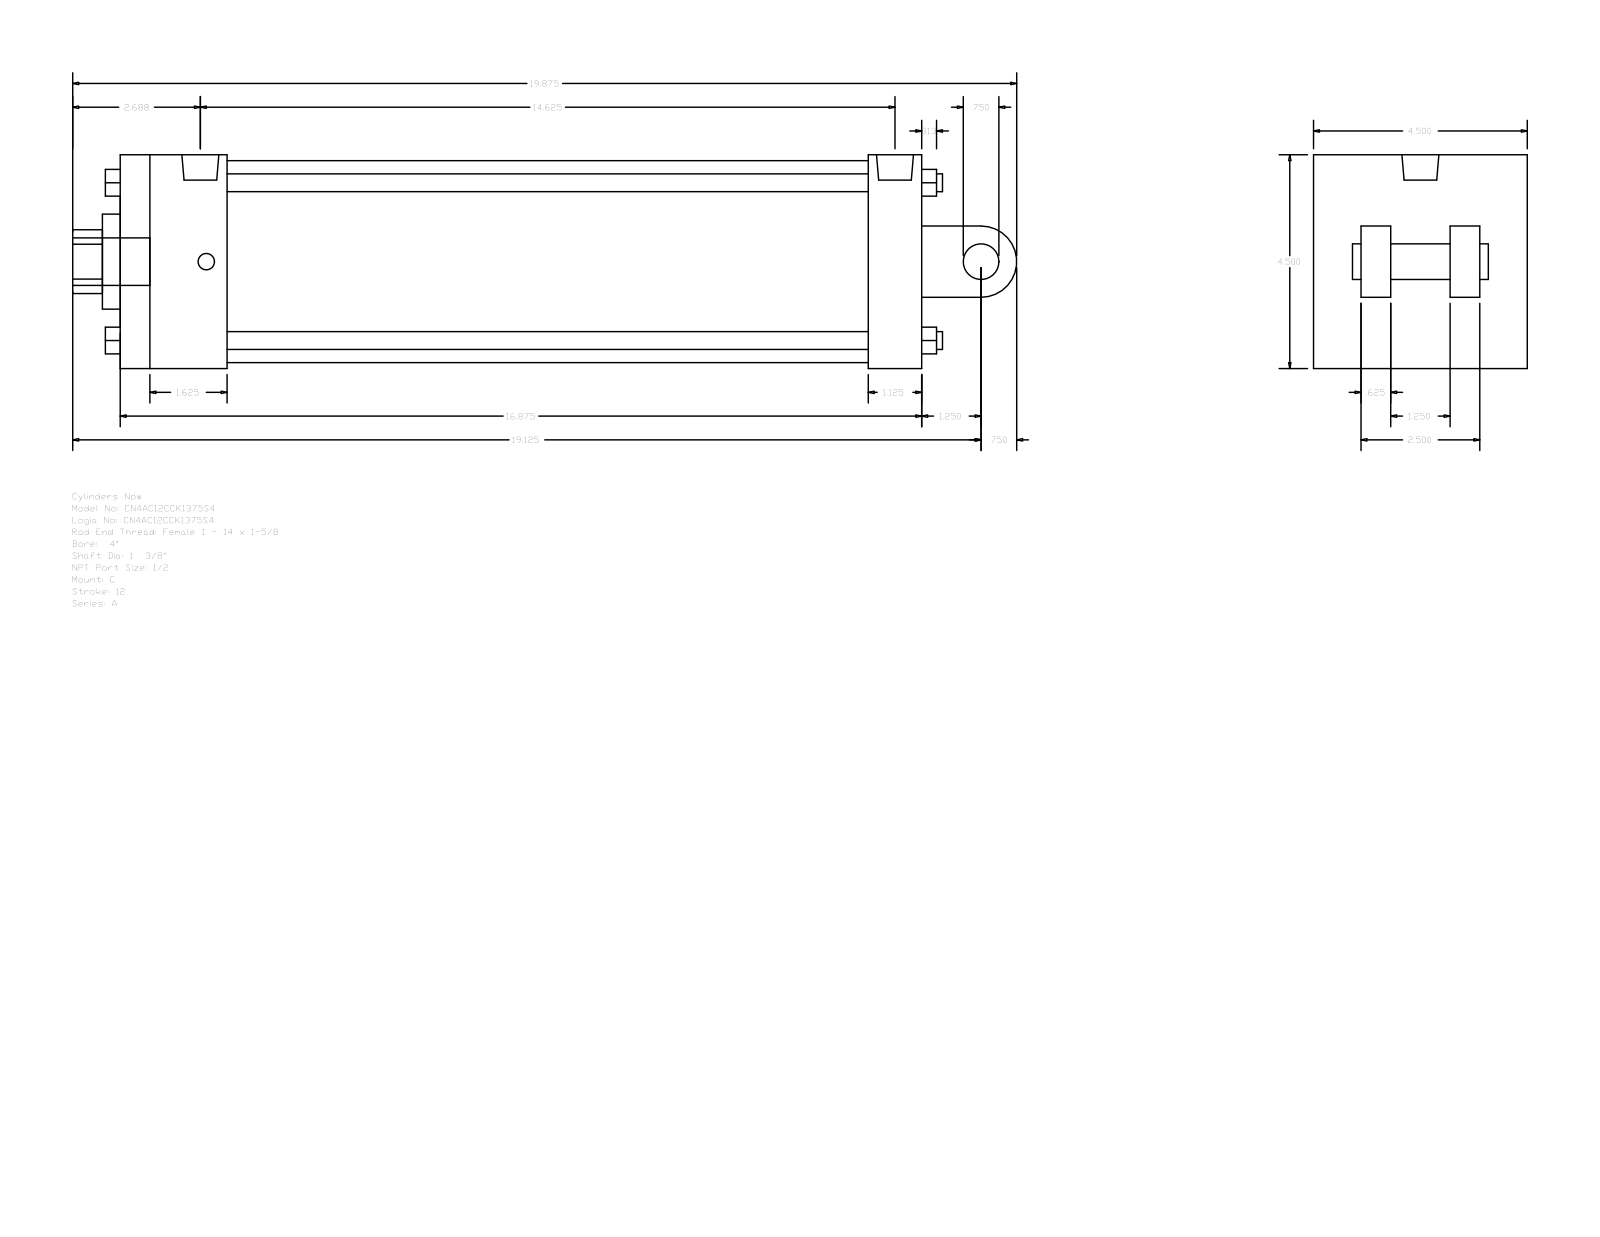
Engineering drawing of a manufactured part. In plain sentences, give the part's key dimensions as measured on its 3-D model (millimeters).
The part is named "A_C__0400_1.375". Its 3-D file was written by "GSSL Pune (CONFIG_CONTROL_DESIGN)". It is 0 solids with 135 faces: 102 planar, 33 cylindrical and 0 other. Overall it measures 504.82 by 114.3 by 114.3 millimeters. Round holes: 2 of diameter 8.73, 1 of diameter 19.77, 1 of diameter 34.92, 1 of diameter 50.8, 1 of diameter 107.95. Round bosses or shafts: 4 of diameter 9.53, 2 of diameter 8.73, 1 of diameter 25.4, 1 of diameter 19.77, 1 of diameter 19.05. Partial cylindrical surfaces (rounded edges, fillets, slot ends): 1 of radius 17.06, 1 of radius 19.05. The main face-to-face distances are 114.3, 428.62, 73.03, 28.57, 400.05, 57.15, 342.9, 371.47, 15.87, 41.27. The hole center spacings are 3.18.
